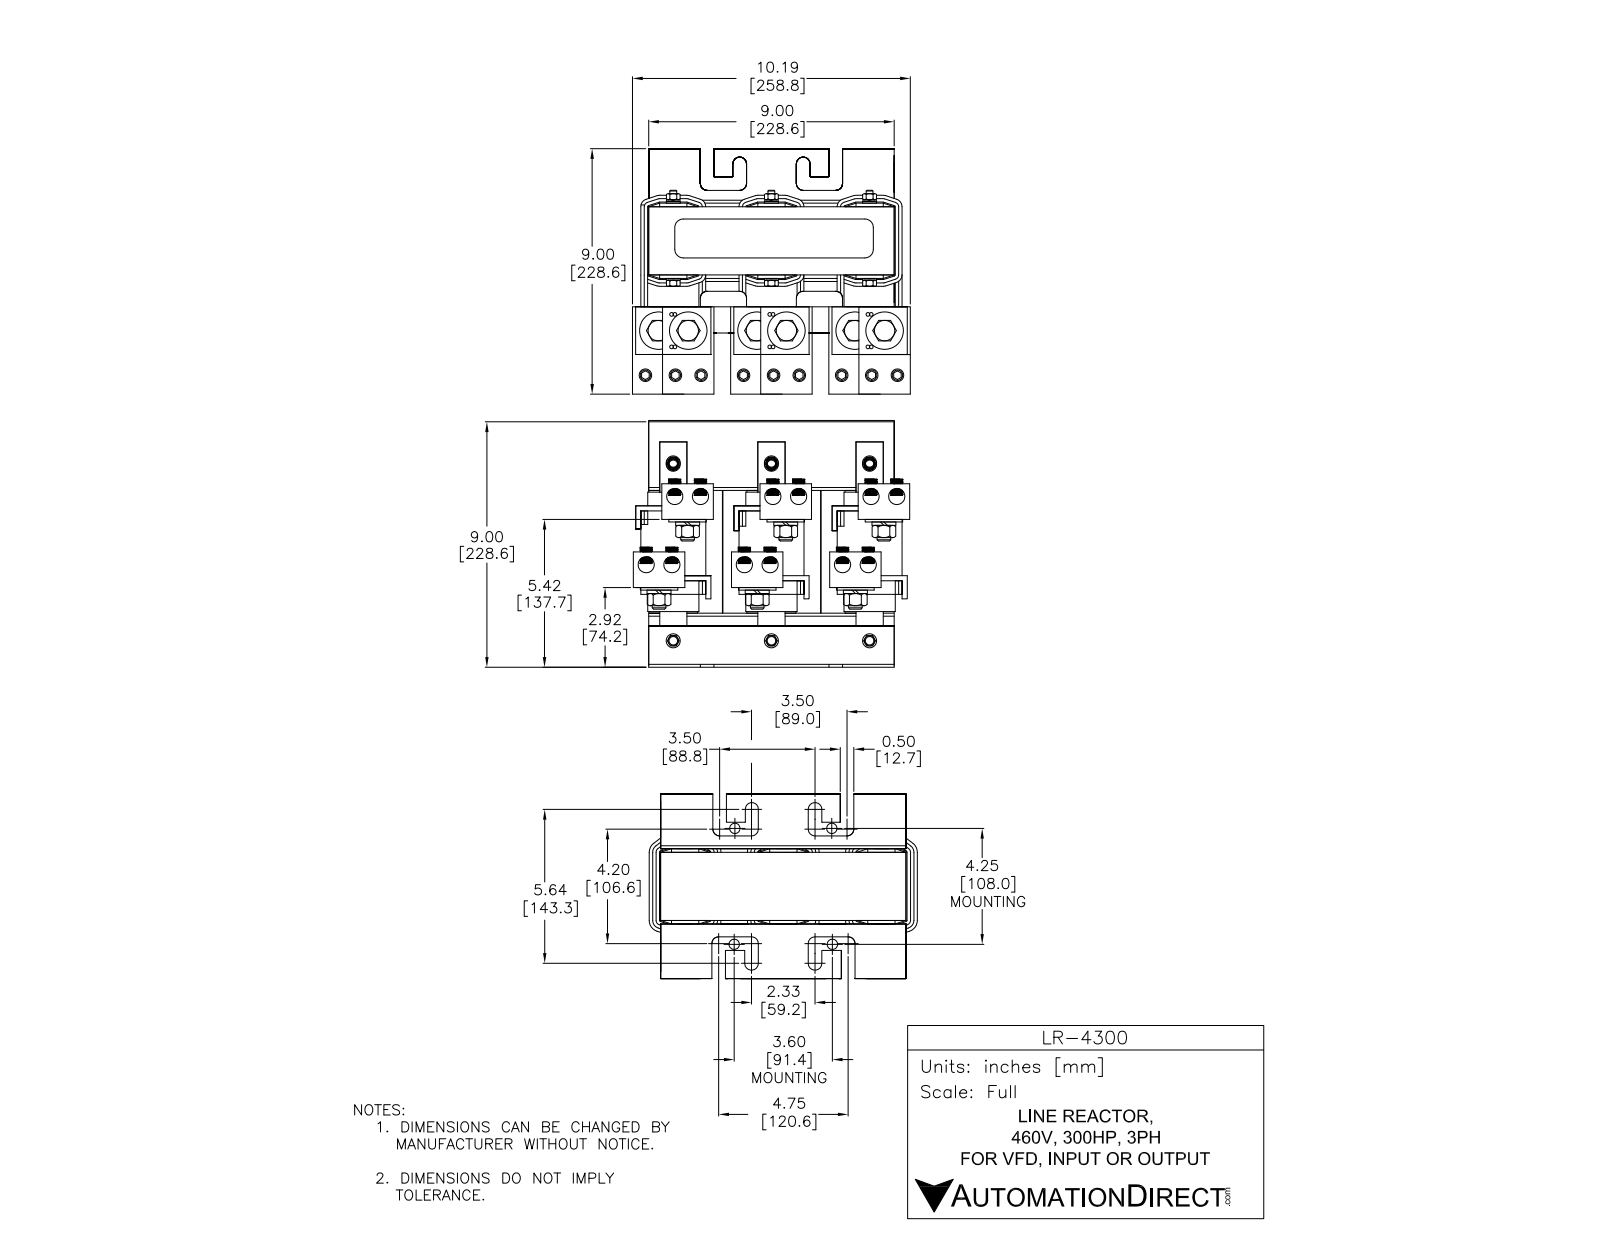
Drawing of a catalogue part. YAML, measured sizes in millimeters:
part_name: "LR-4300"
step_written_by: "SolidWorks 2011 (AUTOMOTIVE_DESIGN)"
units: millimeters
bodies: {solids: 57, faces: 1973, planar: 1066, cylindrical: 883, other: 24}
overall_size: [285.26, 253.32, 213.6]
volume: 5239000
surface_area: 932101
round_holes:
  - {diameter: 15.5, count: 12}
  - {diameter: 19, count: 12}
round_bosses_or_shafts:
  - {diameter: 35, count: 12}
  - {diameter: 15.5, count: 9}
  - {diameter: 19.75, count: 6}
  - {diameter: 14.5, count: 6}
  - {diameter: 12.25, count: 6}
  - {diameter: 6.25, count: 3}
partial_cylinders:
  - {radius: 1, count: 80}
  - {radius: 20.33, count: 48}
  - {radius: 16.34, count: 30}
  - {radius: 119.94, count: 27}
  - {radius: 4.16, count: 21}
  - {radius: 4.37, count: 21}
  - {radius: 7.73, count: 21}
  - {radius: 7.94, count: 21}
face_to_face_distances: [3, 91.75, 63.5, 66.5, 46, 69.5, 183.5, 29.62, 89.62, 75.62]
hole_center_spacings: [91.75, 25, 66.75, 116.75, 183.5, 4.53, 74.72, 87.27]
